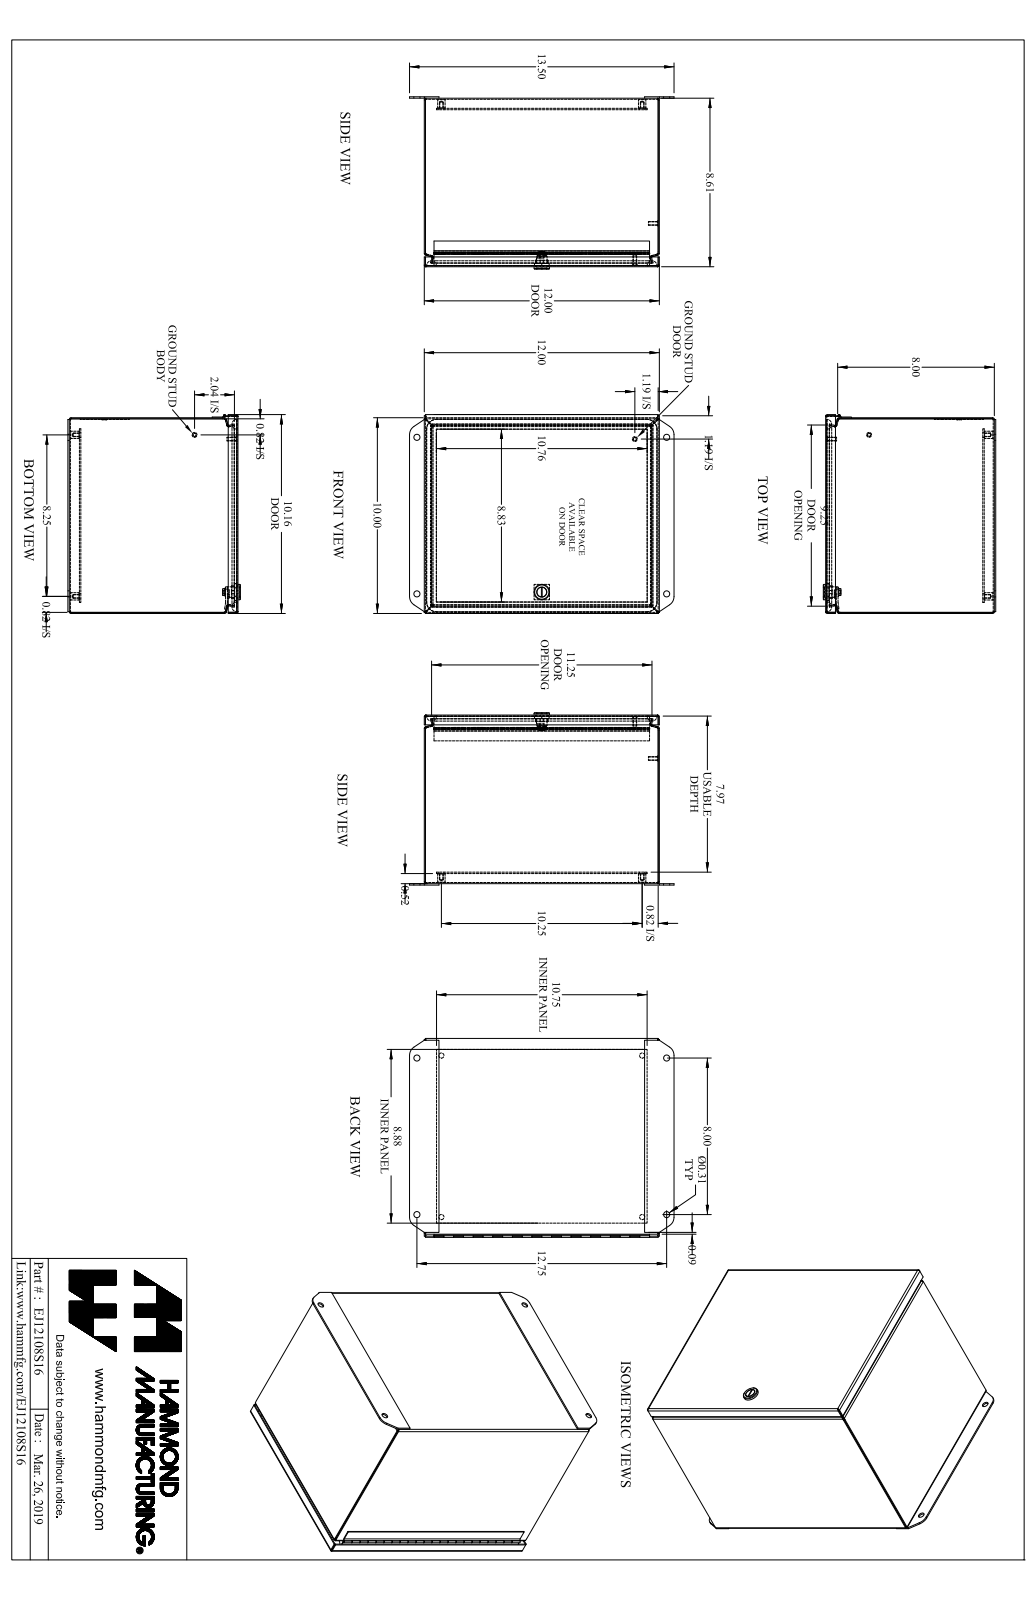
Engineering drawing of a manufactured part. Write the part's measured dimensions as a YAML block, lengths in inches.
part_name: "EJ12108S16_Default"
step_written_by: "SolidWorks 2019 (CONFIG_CONTROL_DESIGN)"
units: inches
bodies: {solids: 16, faces: 628, planar: 326, cylindrical: 222, other: 80}
overall_size: [13.5, 10.165, 8.805]
volume: 50.04
surface_area: 1667
round_holes:
  - {diameter: 0.156, count: 4}
  - {diameter: 0.265, count: 4}
  - {diameter: 0.313, count: 4}
  - {diameter: 0.05, count: 1}
  - {diameter: 0.516, count: 1}
round_bosses_or_shafts:
  - {diameter: 0.375, count: 4}
  - {diameter: 0.25, count: 2}
  - {diameter: 0.19, count: 2}
  - {diameter: 0.788, count: 1}
  - {diameter: 0.535, count: 1}
  - {diameter: 0.496, count: 1}
  - {diameter: 0.435, count: 1}
  - {diameter: 0.1, count: 1}
partial_cylinders:
  - {radius: 0.029, count: 16}
  - {radius: 0.086, count: 16}
  - {radius: 0.281, count: 12}
  - {radius: 0.25, count: 4}
  - {radius: 0.499, count: 4}
  - {radius: 0.5, count: 4}
  - {radius: 0.06, count: 2}
  - {radius: 0.03, count: 1}
face_to_face_distances: [0.057, 8.554, 9.943, 11.943, 0.072, 0.589, 8.611, 8.497, 8.094, 8.037]
hole_center_spacings: [1.256, 11.501, 14.081, 10.25, 8.22, 13.158, 5.13, 6.376]
